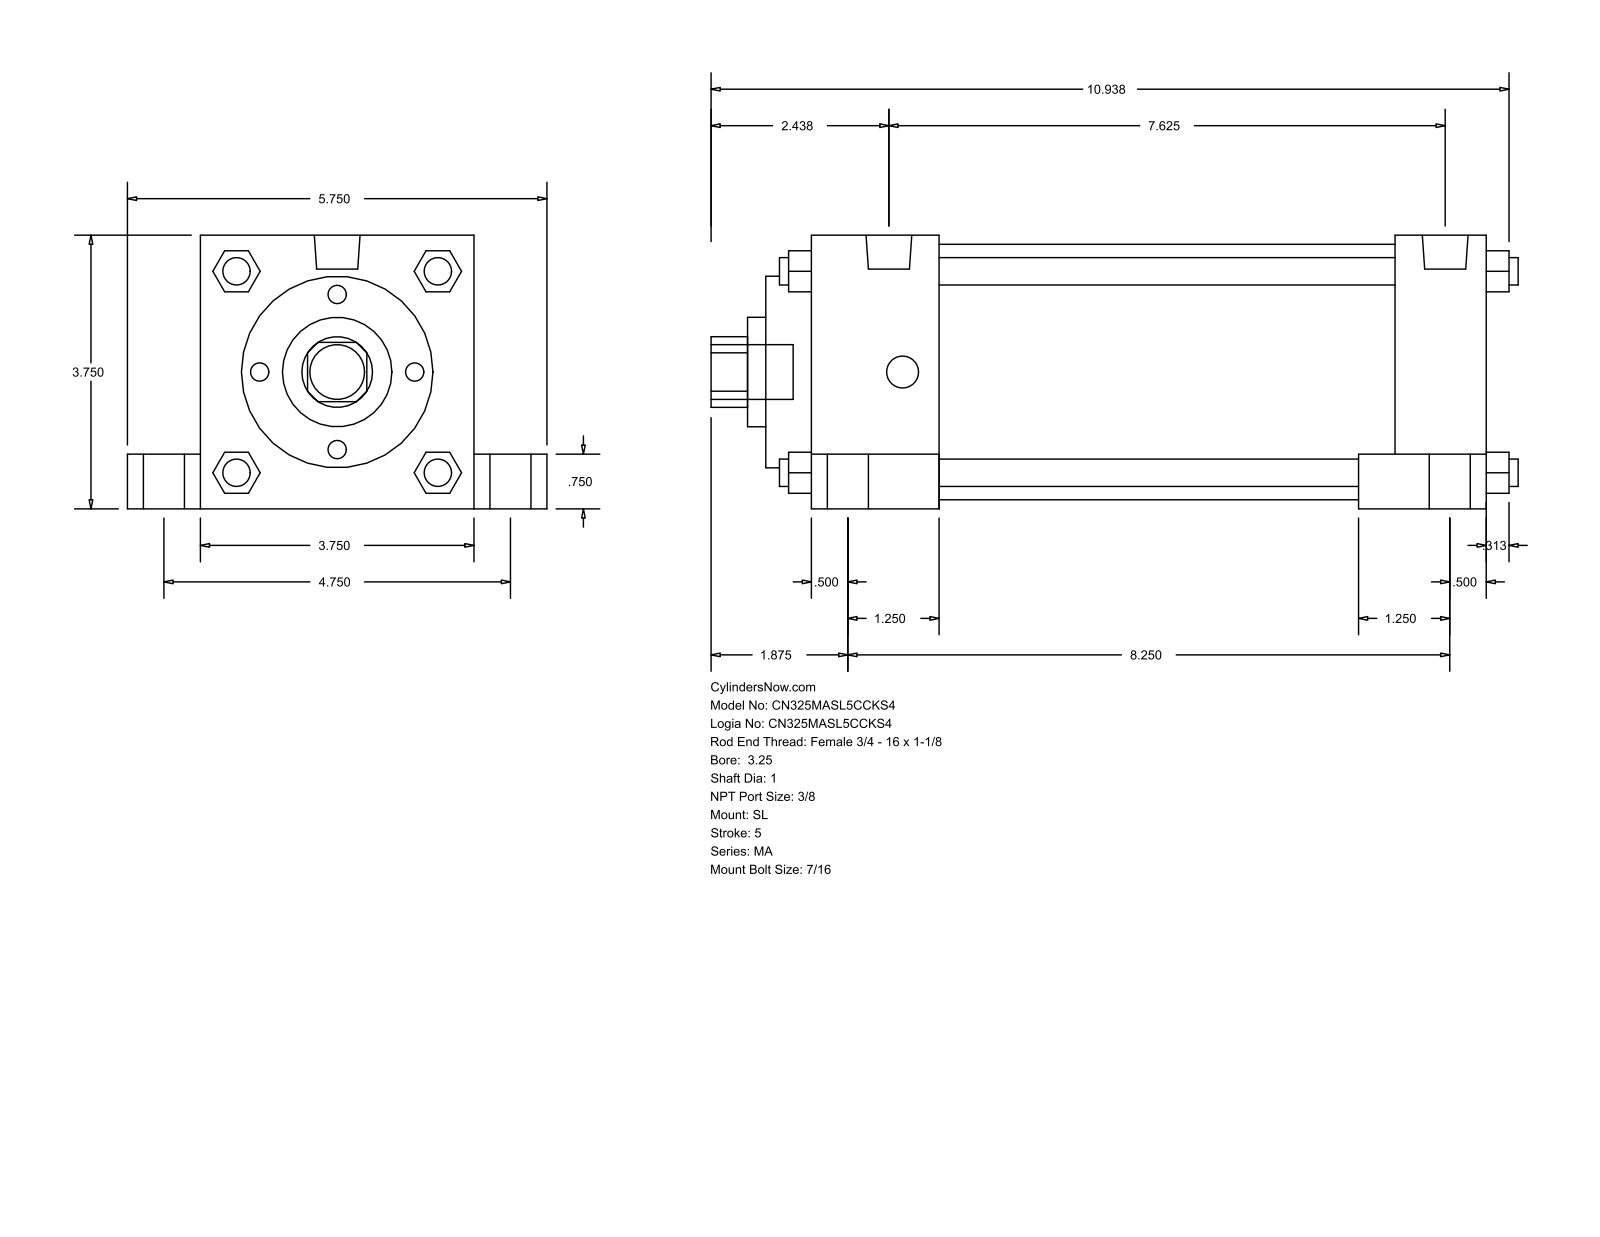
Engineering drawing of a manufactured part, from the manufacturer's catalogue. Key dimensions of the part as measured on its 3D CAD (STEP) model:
Part name (STEP PRODUCT): MA_SL__0325_1
STEP written by: GSSL Pune (CONFIG_CONTROL_DESIGN)
Units: millimetres
Bodies: 0 solids, 150 faces (113 planar, 37 cylindrical, 0 other)
Overall size (bounding box): 280.99 × 146.05 × 95.25
Round holes (diameter × count): ⌀25.4 ×1, ⌀38.1 ×1, ⌀66.67 ×1, ⌀88.9 ×1
Round bosses / shafts (diameter × count): ⌀20.64 ×4, ⌀14.29 ×4, ⌀11.11 ×4, ⌀9.53 ×4, ⌀15.93 ×2, ⌀19.05 ×1
Partial cylindrical surfaces — rounded edges, fillets, slot ends (radius × count): R12.29 ×1
Main face-to-face distances: 95.24, 234.96, 15.87, 25.41, 120.65, 19.05, 203.2, 31.76, 44.46, 158.74
